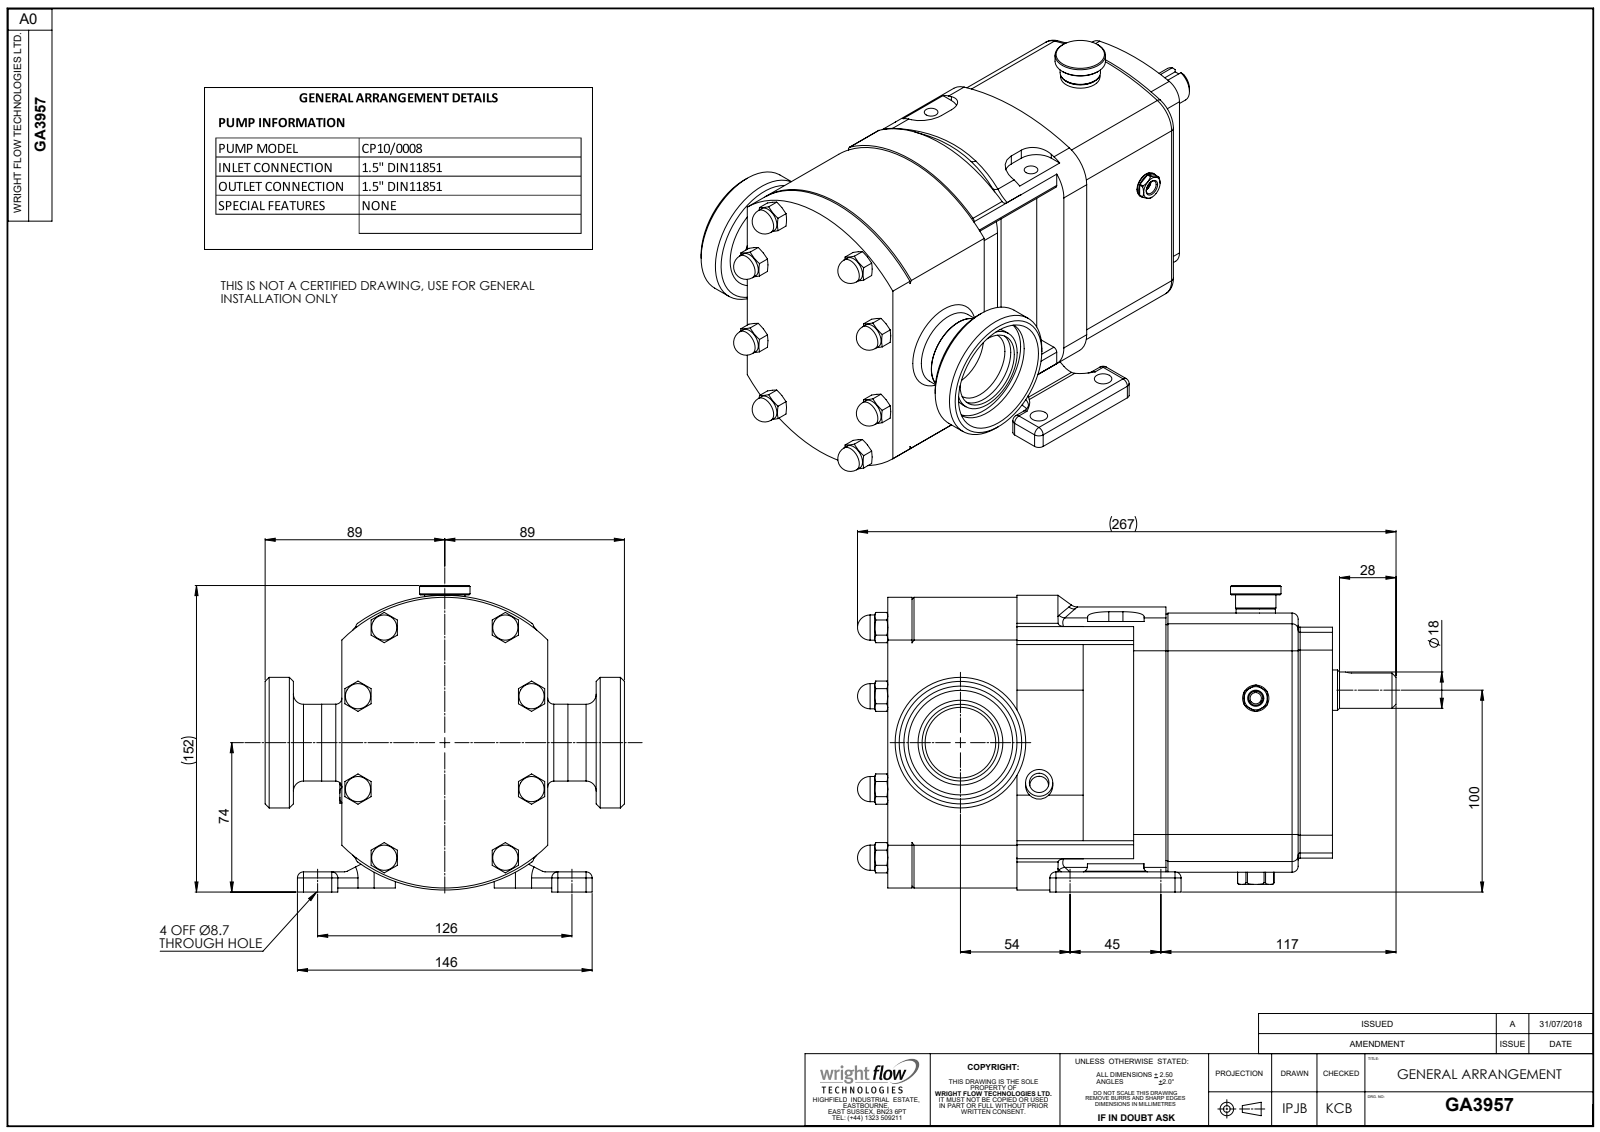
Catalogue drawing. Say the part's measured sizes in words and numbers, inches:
The part is named "Copy (2) of CP10-0008-08 H T^GA3957; GA3957; Copy of Z94-5031-22 - 1.5 INCH DIN11851^GA3957". Its 3-D file was written by "SolidWorks 2023 (AUTOMOTIVE_DESIGN)". It is 3 solids with 776 faces: 258 planar, 230 cylindrical and 288 other. Overall it measures 10.526 by 7.008 by 5.977 inches. Its volume is 152.2 cubic inches and its surface area 310.1 square inches. Round holes: 4 of diameter 0.343, 4 of diameter 0.551, 2 of diameter 0.3, 2 of diameter 0.315, 1 of diameter 0.887, 1 of diameter 1.372, 1 of diameter 1.378, 1 of diameter 1.496, 1 of diameter 2.039. Round bosses or shafts: 2 of diameter 1.181, 1 of diameter 2.547, 1 of diameter 1.654, 1 of diameter 1.5, 1 of diameter 0.985, 1 of diameter 0.787, 1 of diameter 0.787, 1 of diameter 0.768. Partial cylindrical surfaces (rounded edges, fillets, slot ends): 30 of radius 0.079, 26 of radius 0.118, 12 of radius 0.531, 8 of radius 0.413, 6 of radius 0.138, 4 of radius 0.217, 4 of radius 0.236, 4 of radius 0.354. The main face-to-face distances are 0.197, 4.882, 8.715, 4.016, 3.819, 0.197, 3.622, 3.819, 3.833, 0.079. The hole center spacings are 1.414, 3.959, 1.772, 2.992, 3.032, 4.26, 4.961, 5.267.
